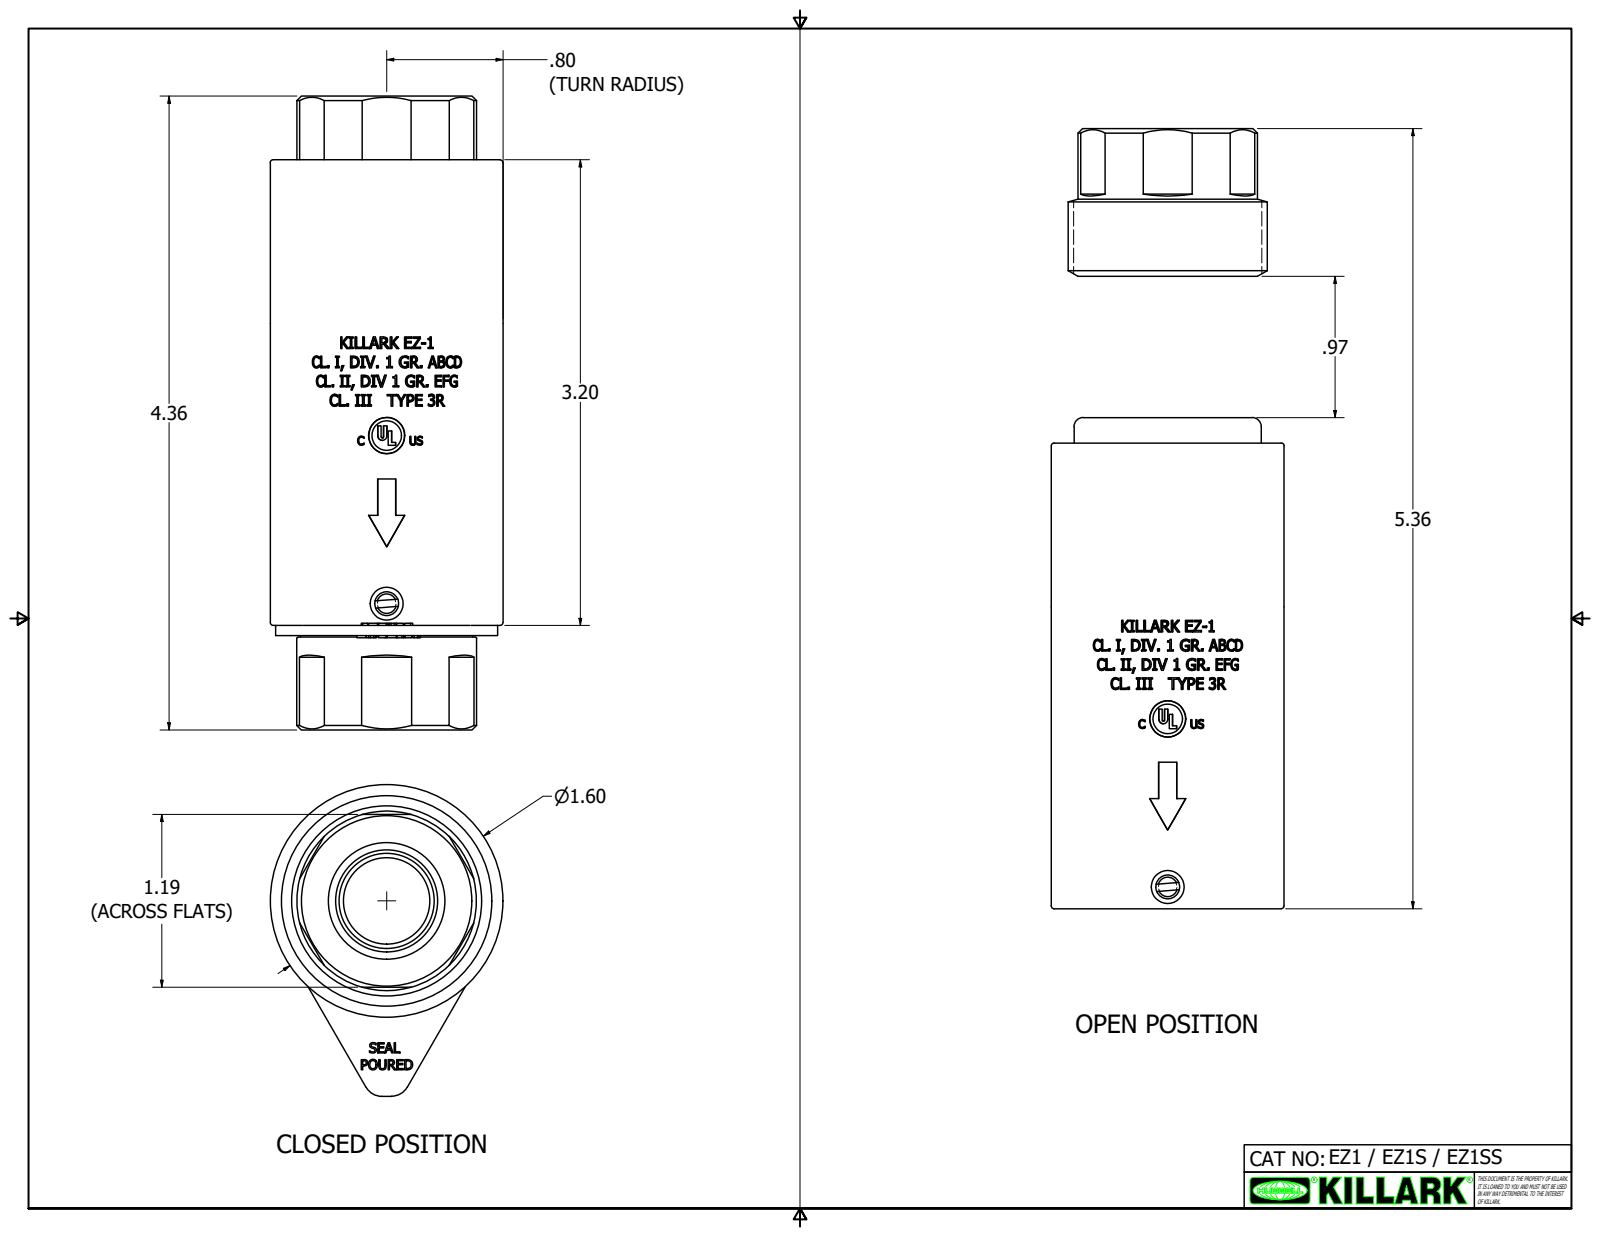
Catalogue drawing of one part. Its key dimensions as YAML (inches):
part_name: "51991-1_Shrinkwrap_1"
step_written_by: "Autodesk Inventor 2020 (AUTOMOTIVE_DESIGN)"
units: inches
bodies: {solids: 5, faces: 1271, planar: 688, cylindrical: 114, other: 469}
overall_size: [4.355, 2.143, 1.6]
volume: 4.591
surface_area: 59.51
round_holes:
  - {diameter: 0.164, count: 1}
  - {diameter: 0.595, count: 1}
  - {diameter: 1, count: 1}
  - {diameter: 1.066, count: 1}
  - {diameter: 1.126, count: 1}
  - {diameter: 1.186, count: 1}
  - {diameter: 1.288, count: 1}
  - {diameter: 1.307, count: 1}
  - {diameter: 1.328, count: 1}
  - {diameter: 1.367, count: 1}
round_bosses_or_shafts:
  - {diameter: 1.6, count: 1}
  - {diameter: 1.369, count: 1}
  - {diameter: 1.286, count: 1}
  - {diameter: 1.236, count: 1}
  - {diameter: 1.234, count: 1}
  - {diameter: 1.186, count: 1}
  - {diameter: 1.185, count: 1}
partial_cylinders:
  - {radius: 0.075, count: 2}
  - {radius: 0.1, count: 2}
  - {radius: 0.125, count: 2}
  - {radius: 0.609, count: 1}
  - {radius: 0.656, count: 1}
  - {radius: 0.763, count: 1}
  - {radius: 0.79, count: 1}
face_to_face_distances: [1.187, 2.622, 0.07, 2.692, 1.015, 3.637, 3.707, 4.355, 3.34, 0.718]
